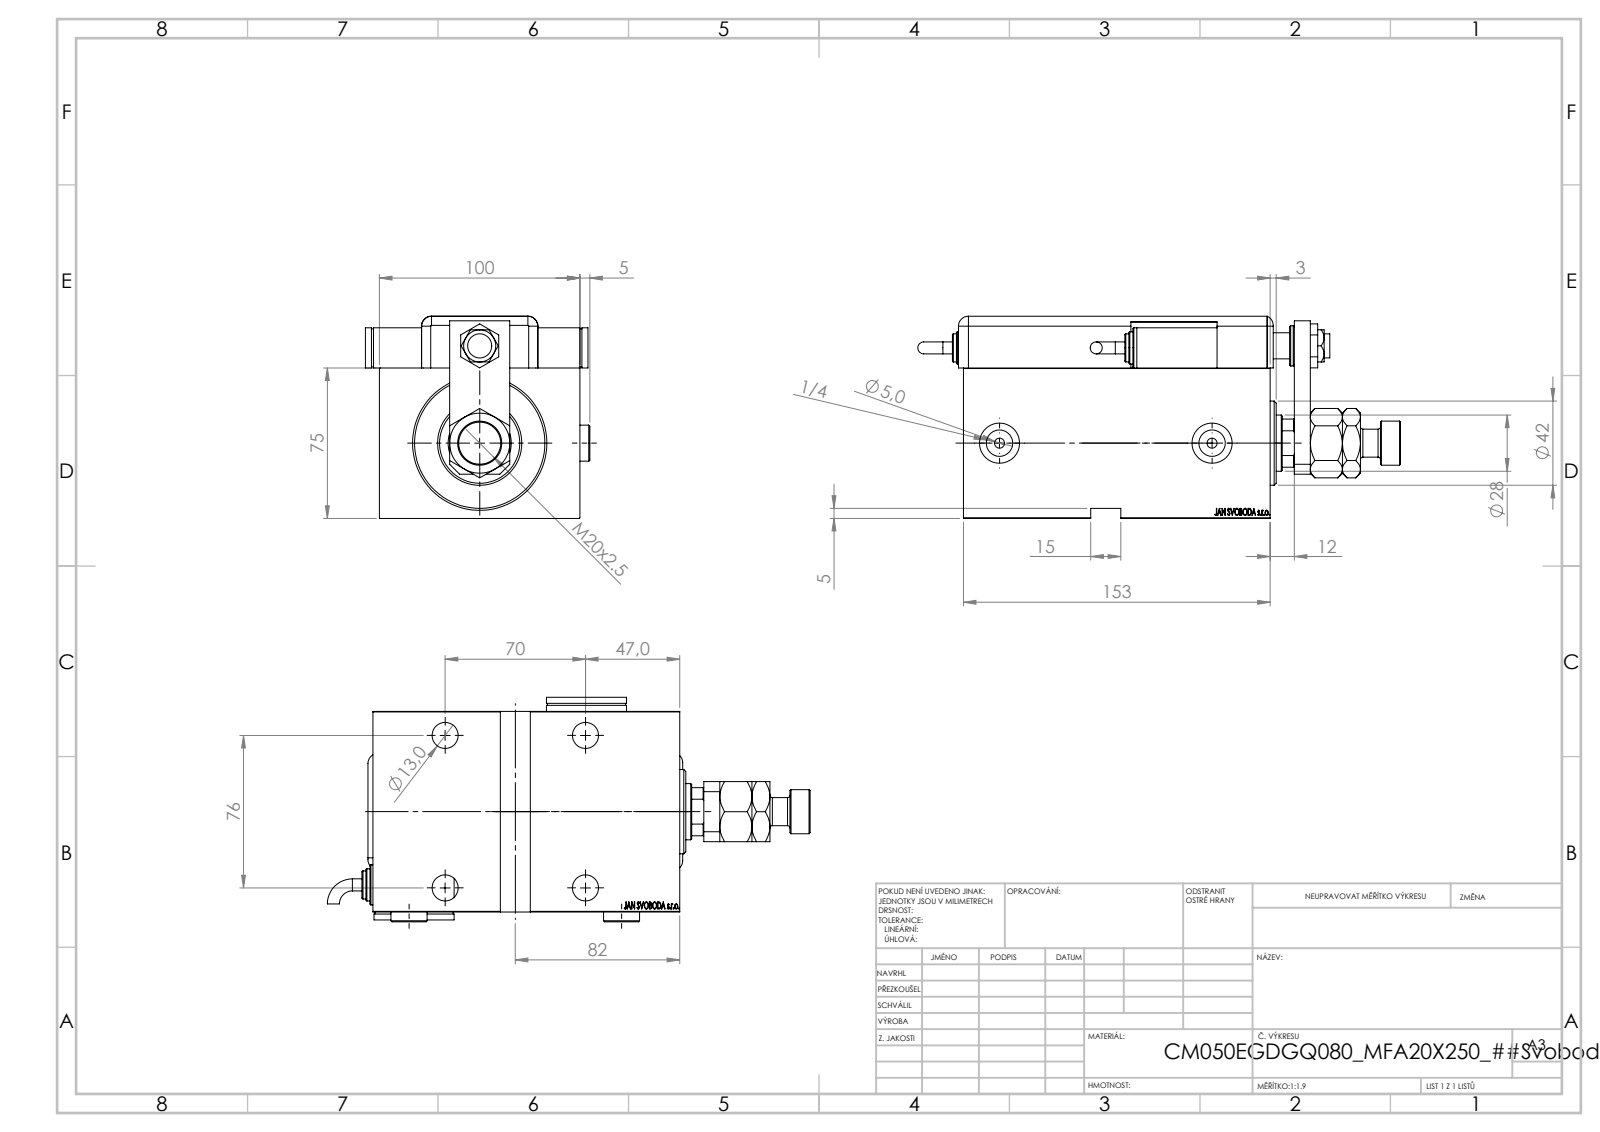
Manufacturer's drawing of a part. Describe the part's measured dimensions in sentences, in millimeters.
The part is named "Zatka_OIL_PORT; SWITCH DIM A_G; NUT_D13; V450CM_VC_B (+7 more)". Its 3-D file was written by "SolidWorks 2019 (CONFIG_CONTROL_DESIGN)". It is 16 solids with 1348 faces: 668 planar, 127 cylindrical and 553 other. Overall it measures 240.76 by 111.9 by 100.8 millimeters. Its volume is 1 175 000 cubic millimeters and its surface area 214 395 square millimeters. Round holes: 5 of diameter 13, 4 of diameter 19, 3 of diameter 20, 2 of diameter 4, 2 of diameter 5, 2 of diameter 8, 2 of diameter 13.16, 1 of diameter 12, 1 of diameter 14, 1 of diameter 18.5, 1 of diameter 28, 1 of diameter 31.5. Round bosses or shafts: 3 of diameter 20, 3 of diameter 14, 2 of diameter 18, 2 of diameter 16, 2 of diameter 6, 1 of diameter 52, 1 of diameter 42, 1 of diameter 22. Partial cylindrical surfaces (rounded edges, fillets, slot ends): 9 of radius 5, 1 of radius 10, 1 of radius 13.5. The main face-to-face distances are 3, 75, 100, 100.8, 25.8, 14, 20, 153, 22.8, 97.8. The hole center spacings are 47.2, 61.22, 70, 76, 103.32, 111.57, 118.19, 20.
